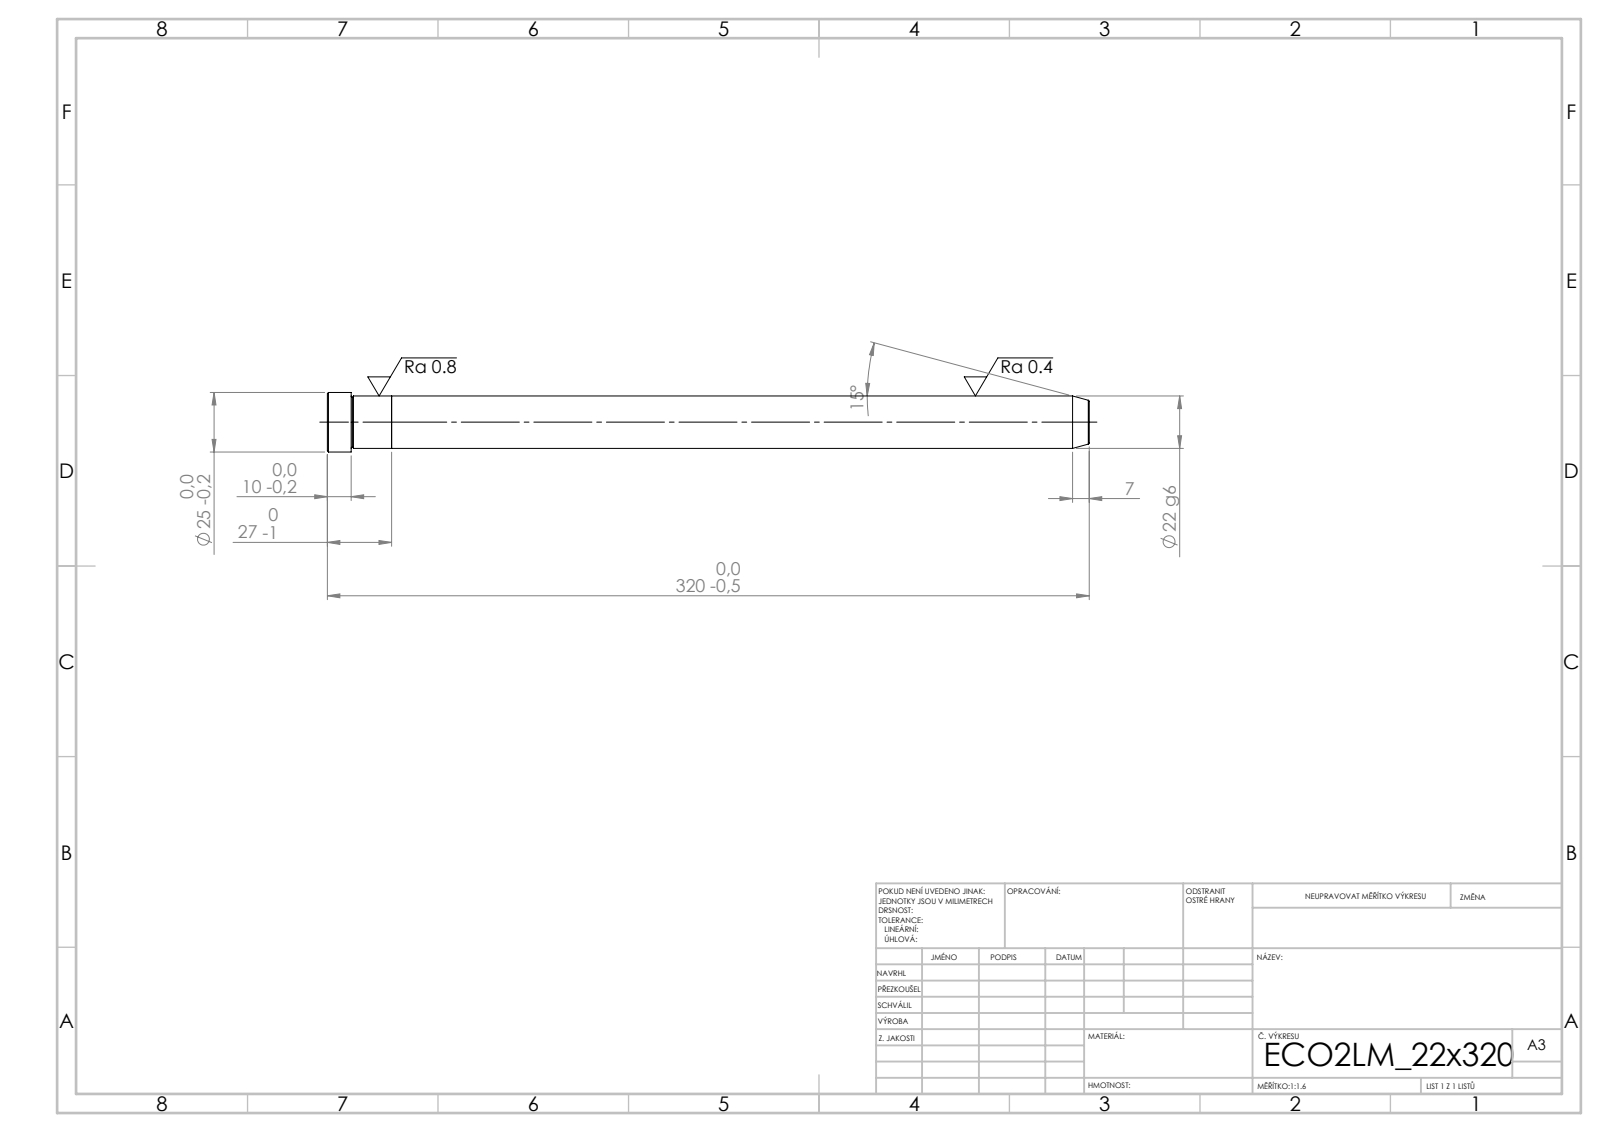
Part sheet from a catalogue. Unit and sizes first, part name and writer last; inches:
Units: inches
Overall size (bounding box): 12.598 × 0.984 × 0.984
Round bosses / shafts (diameter × count): ⌀0.984 ×1, ⌀0.866 ×1
Main face-to-face distances: 1.063, 11.535, 12.598, 12.205, 0.669, 0.394
Volume: 7.462 in³ · Surface area: 36.91 in²
Bodies: 2 solids, 21 faces (5 planar, 6 cylindrical, 10 other)
STEP written by: SolidWorks 2019 (CONFIG_CONTROL_DESIGN)
